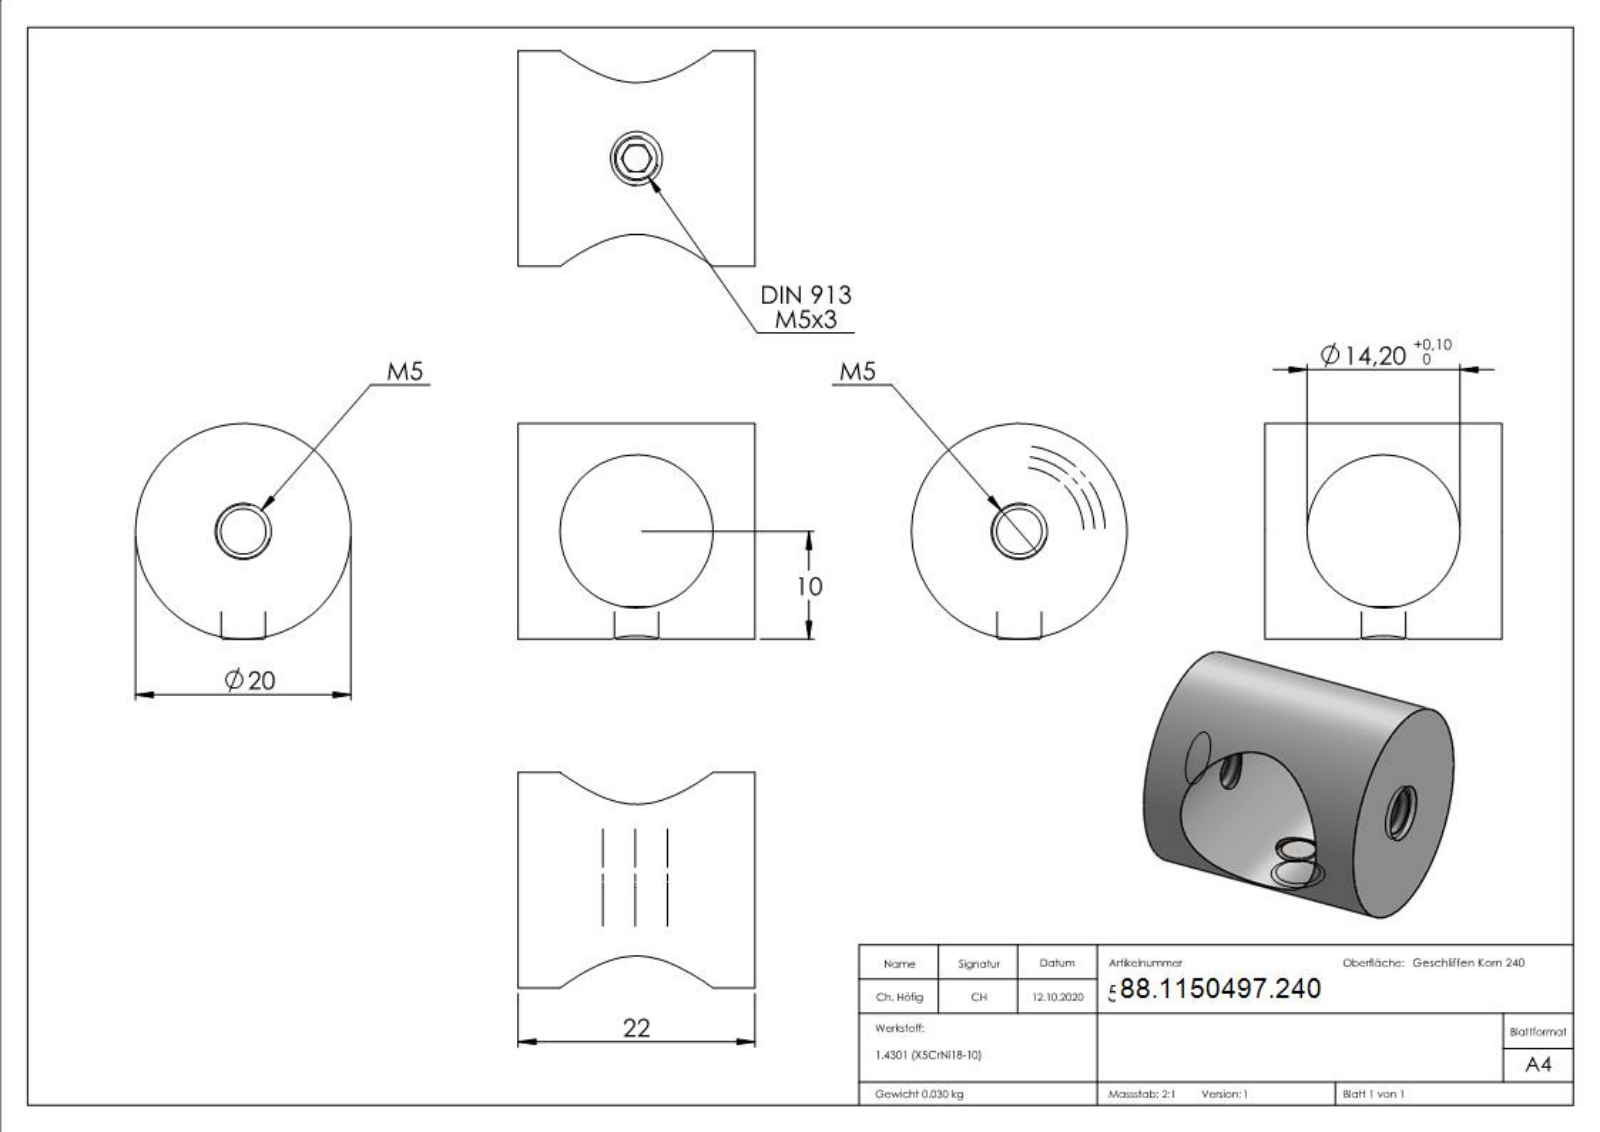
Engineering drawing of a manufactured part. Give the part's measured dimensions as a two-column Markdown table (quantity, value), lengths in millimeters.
| quantity | value |
| --- | --- |
| part name | 5049X-240 Teil1; DIN913; 50497-240; 5049X-240 Teil1_50497-240 Teil1 (+1 more) |
| STEP written by | SolidWorks 2018 (CONFIG_CONTROL_DESIGN) |
| units | millimeters |
| bodies | 2 solids, 259 faces (121 planar, 37 cylindrical, 101 other) |
| overall size | 70 × 22 × 20 |
| volume | 3 842 mm³ |
| surface area | 2 579 mm² |
| round holes (diameter × count) | 4.2 × 2, 14.2 × 1 |
| round bosses / shafts (diameter × count) | 20 × 1, 5 × 1 |
| partial cylindrical surfaces (radius × count) | 7.2 × 1 |
| main face-to-face distances | 22, 2.5, 3, 2, 1, 11, 0.35, 1.19, 0.53, 10.82 |
